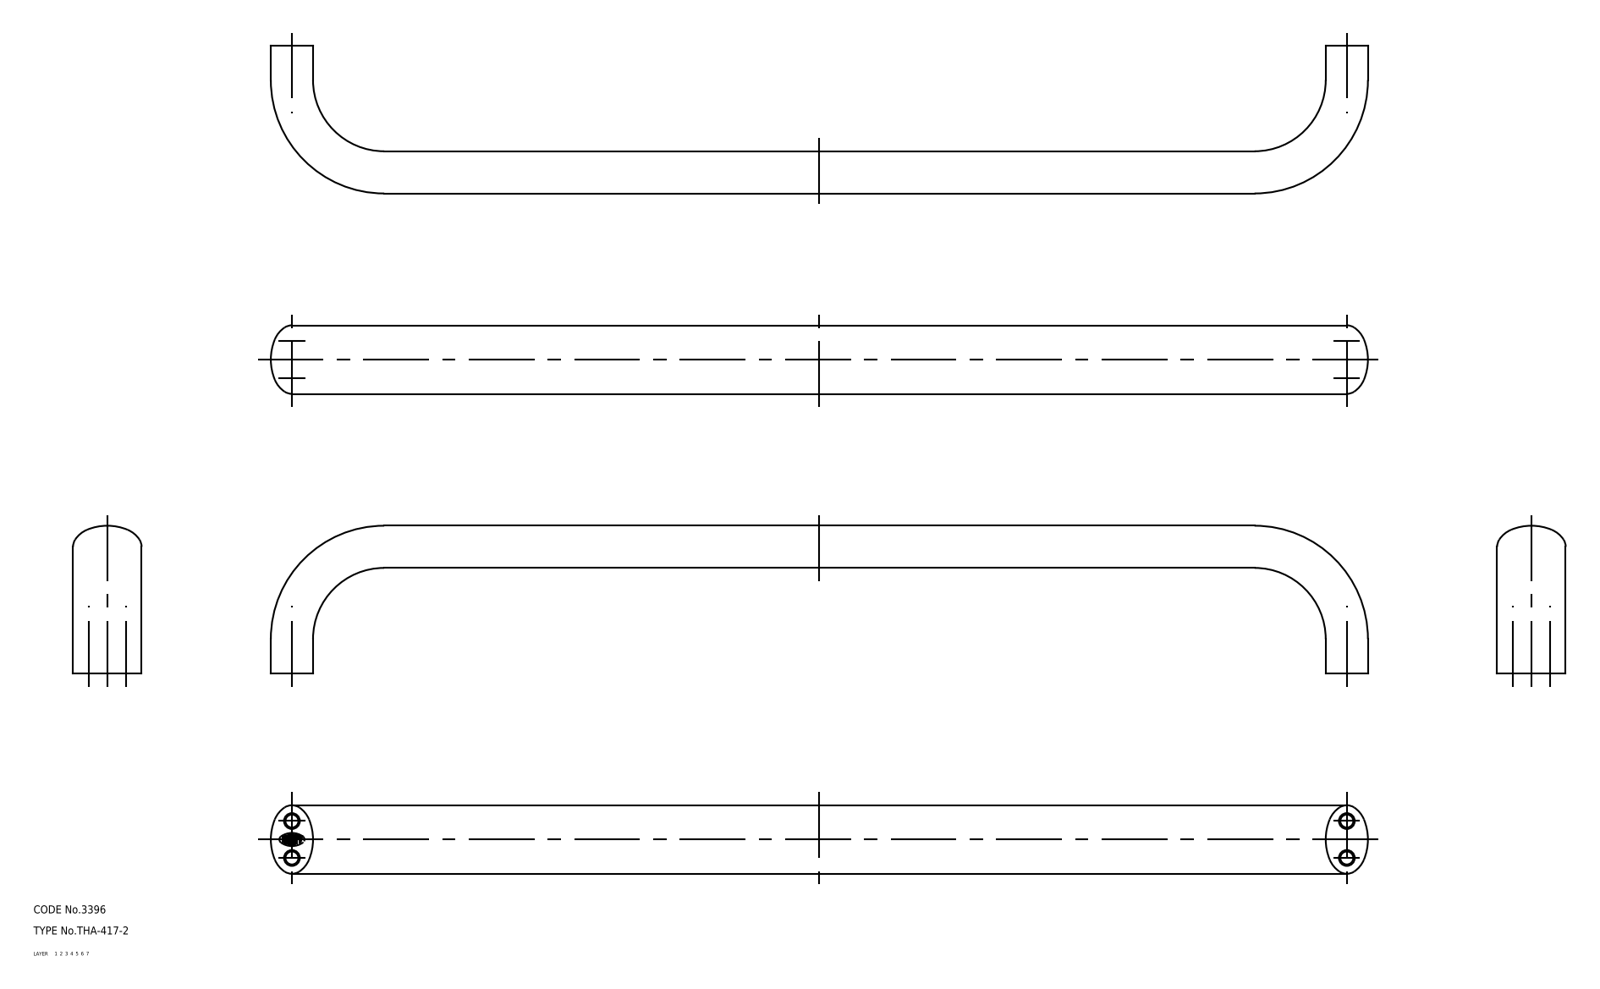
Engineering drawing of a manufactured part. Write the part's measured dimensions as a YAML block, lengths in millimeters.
part_name: "pull"
step_written_by: "CADfix (AUTOMOTIVE_DESIGN)"
units: millimeters
bodies: {solids: 1, faces: 24, planar: 0, cylindrical: 0, other: 24}
overall_size: [416, 56, 26]
volume: 149948
surface_area: 33336
